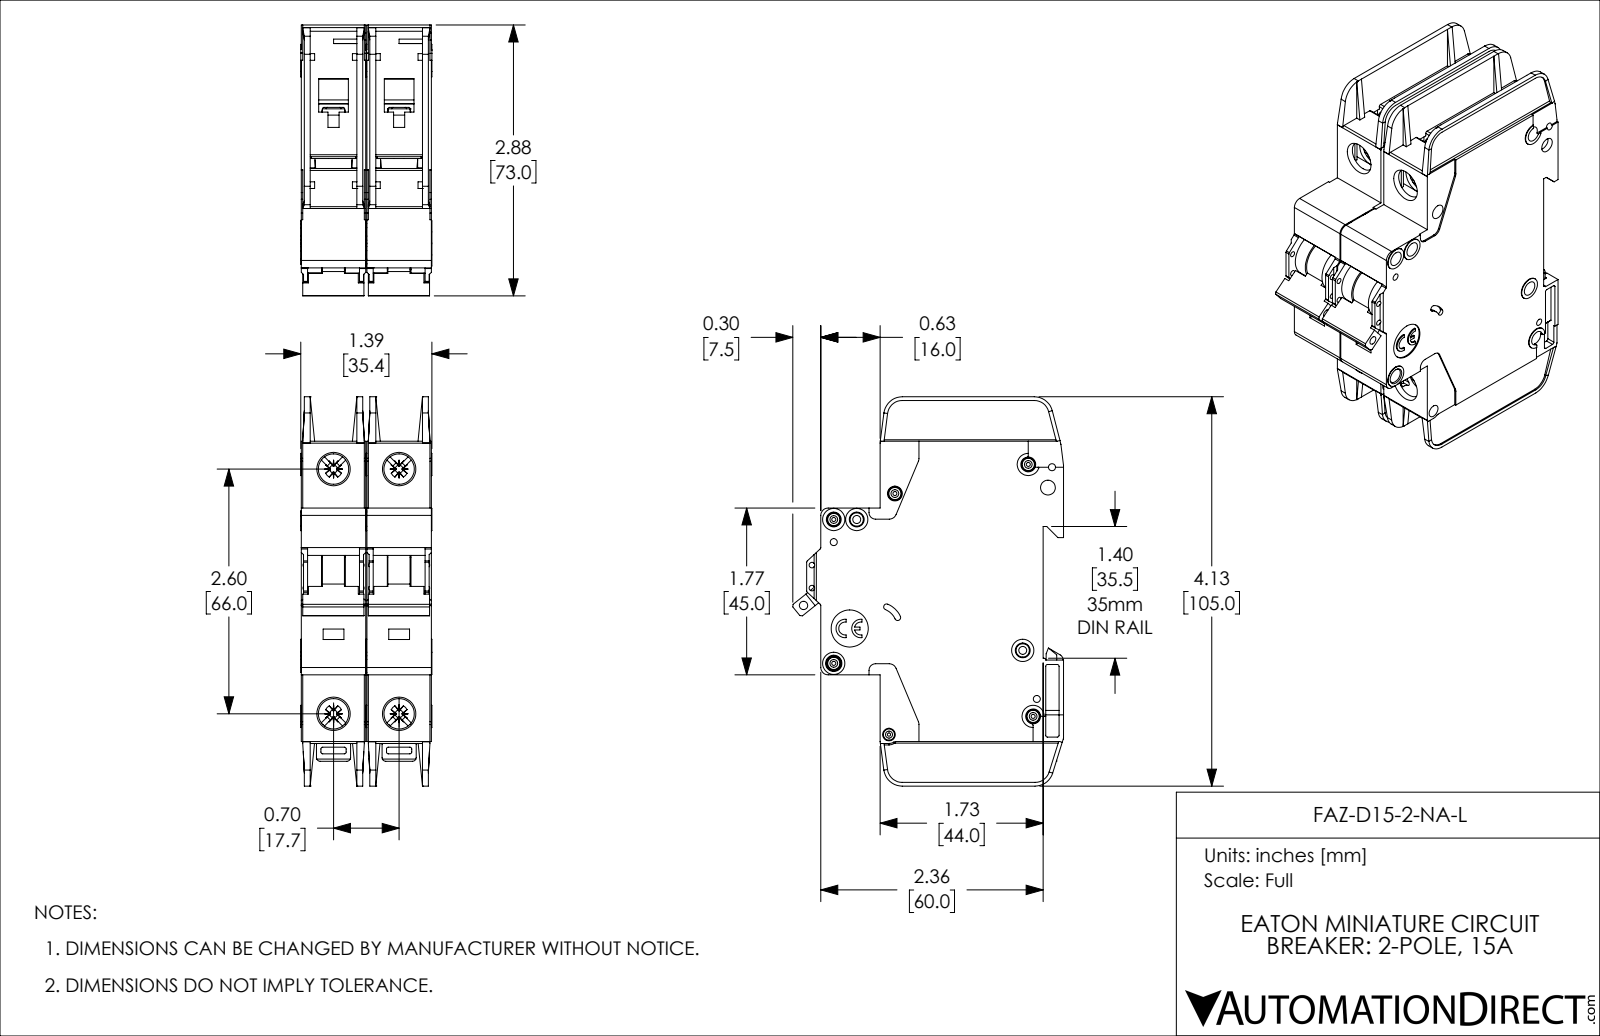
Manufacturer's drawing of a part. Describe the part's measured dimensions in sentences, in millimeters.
The part is named "FAZ-D15-2-NA-L". Its 3-D file was written by "SolidWorks 2019 (AUTOMOTIVE_DESIGN)". It is 2 solids with 2254 faces: 1342 planar, 714 cylindrical and 198 other. Overall it measures 105 by 73.1 by 35.4 millimeters. Its volume is 153 500 cubic millimeters and its surface area 52 910 square millimeters. Round holes: 8 of diameter 4, 5 of diameter 1.1, 4 of diameter 1.9, 4 of diameter 8.2, 2 of diameter 1.5, 2 of diameter 2.2, 1 of diameter 0.9, 1 of diameter 2.3, 1 of diameter 2.5, 1 of diameter 3.4, 1 of diameter 10. Round bosses or shafts: 5 of diameter 3.3, 4 of diameter 6, 3 of diameter 3, 2 of diameter 2.5. Partial cylindrical surfaces (rounded edges, fillets, slot ends): 57 of radius 0.5, 20 of radius 0.4, 14 of radius 1, 10 of radius 2, 8 of radius 1.1, 5 of radius 0.2, 5 of radius 5, 4 of radius 0.3. The main face-to-face distances are 17.7, 1.2, 17.4, 15, 2.4, 16.2, 13.8, 35.1, 18.9, 16.5. The hole center spacings are 6.2, 13.6, 17.7, 22.1, 66, 68.3, 4.8, 5.1.
